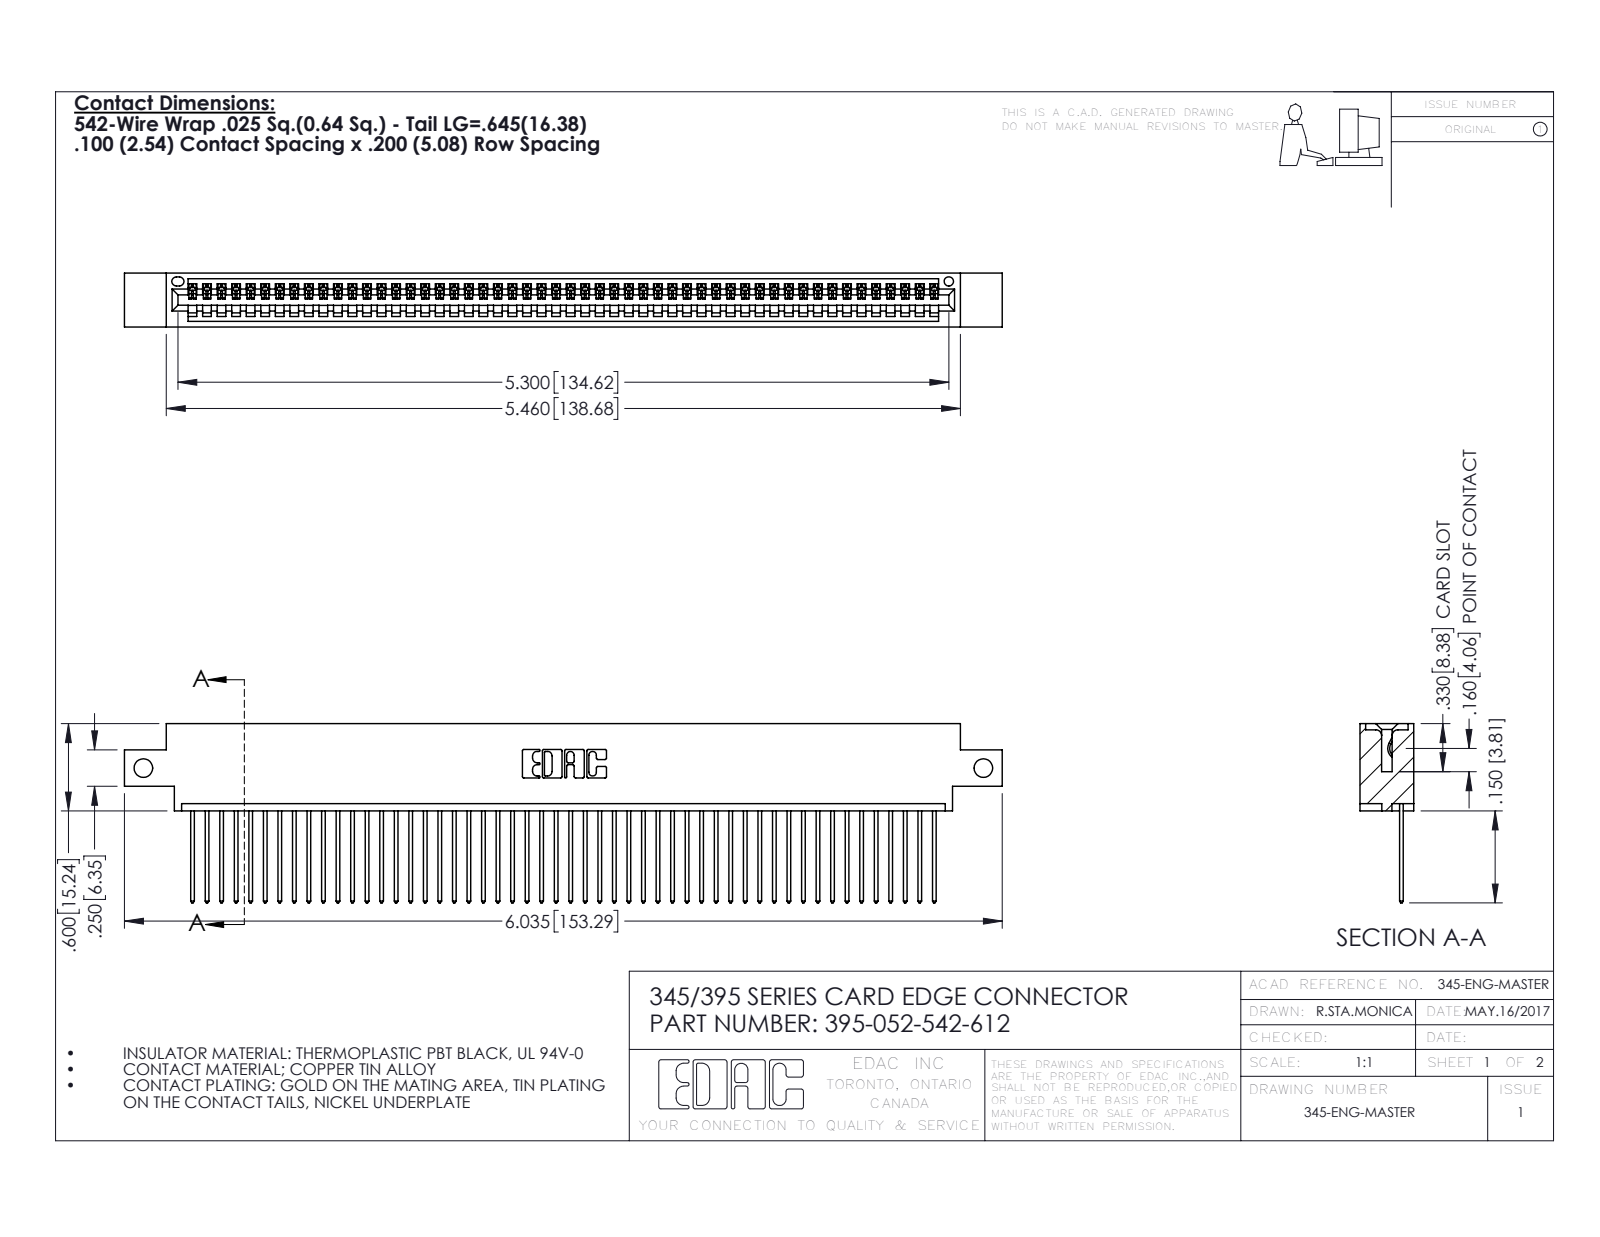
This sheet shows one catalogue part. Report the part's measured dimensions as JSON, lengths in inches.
{"part_name": "345 Part_0.170 Offset - Side Mount; 395-052-542-612; 345-292-001_345-293-142", "step_written_by": "SolidWorks 2016 (CONFIG_CONTROL_DESIGN)", "units": "inches", "bodies": {"solids": 53, "faces": 3146, "planar": 2164, "cylindrical": 982, "other": 0}, "overall_size": [6.035, 1.232, 0.37], "volume_in3": 0.888, "surface_area_in2": 31.3, "round_holes": [[0.128, 2], [0.064, 1]], "partial_cylinders_radius": [[0.006, 104], [0.01, 104], [0.01, 22], [0.007, 6], [0.031, 6], [0.026, 3], [0.031, 2], [0.04, 2]], "face_to_face_distances": [0.072, 0.298, 0.37, 0.098, 0.272, 0.025, 0.2, 0.225, 0.175, 0.149], "hole_center_spacings": [5.775]}
